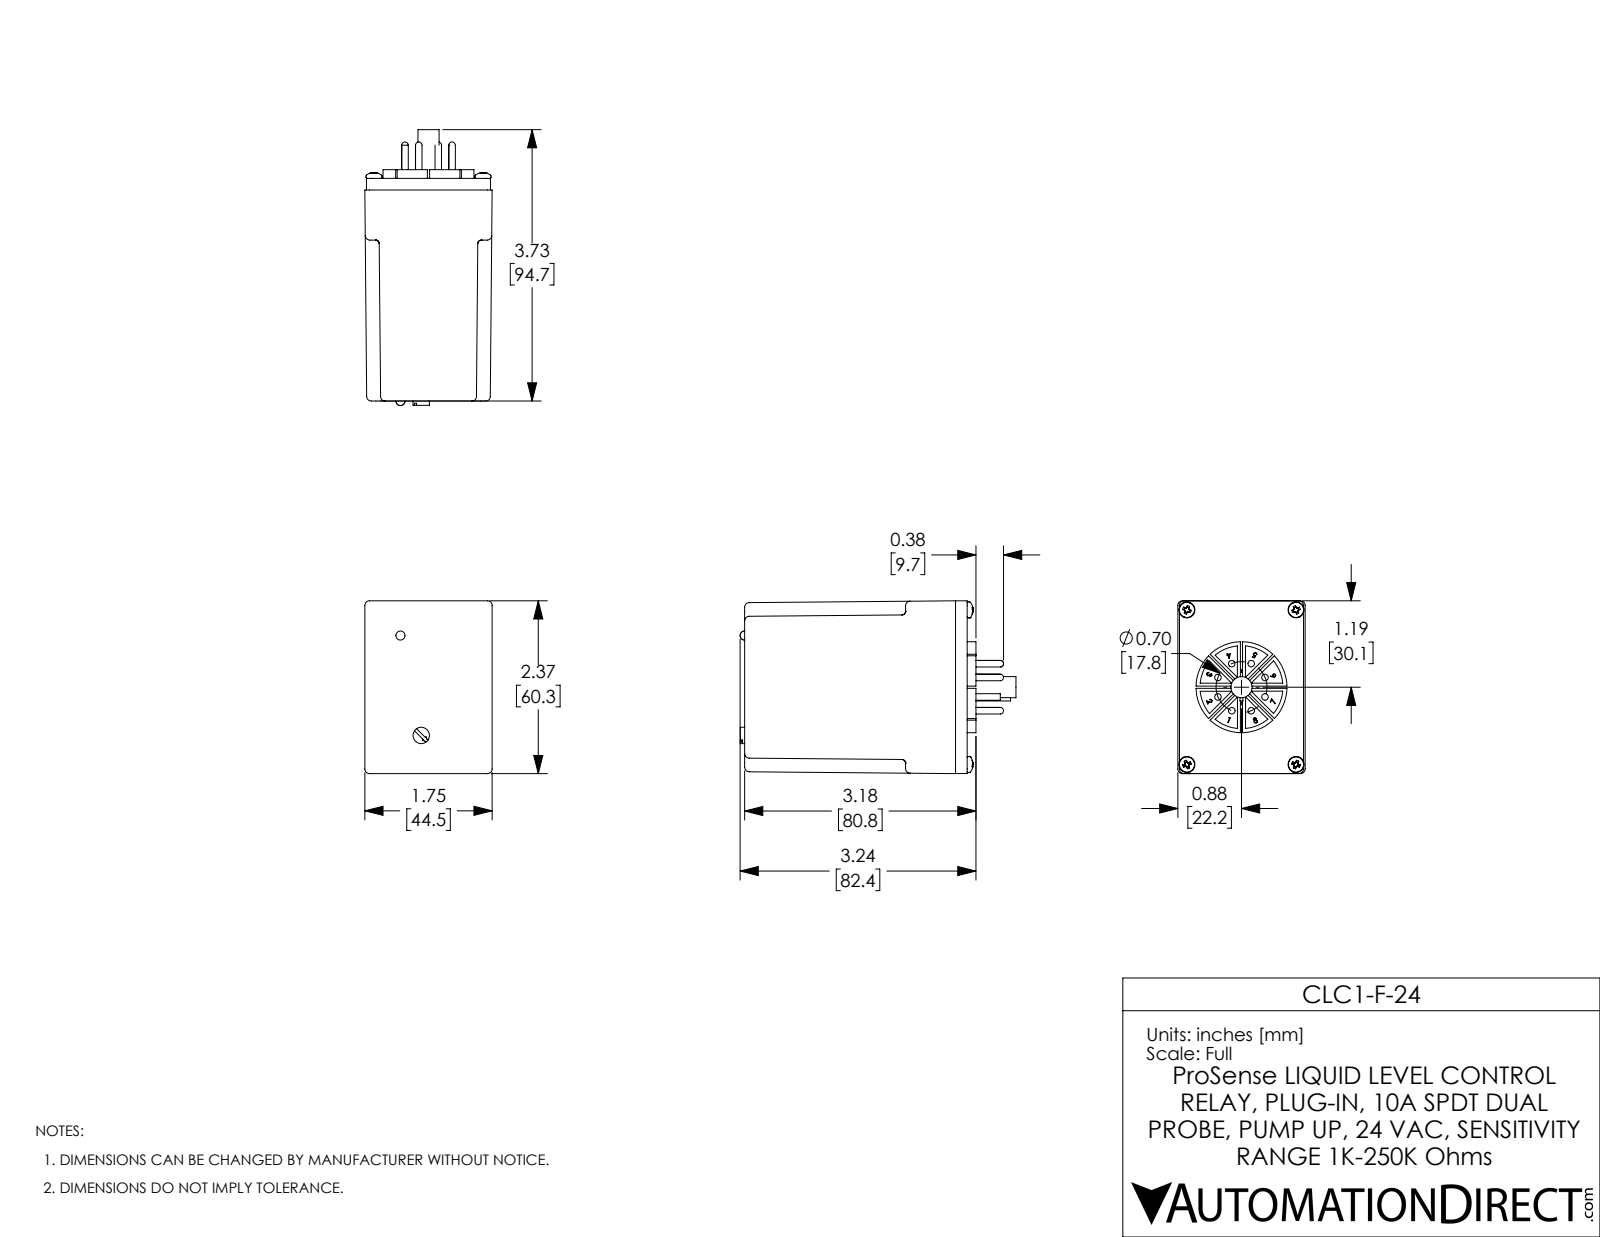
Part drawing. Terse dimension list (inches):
name: CLC1-F-24
written by: SolidWorks 2017 (AUTOMOTIVE_DESIGN)
unit: in
bodies: 16 solids, 706 faces (229 planar, 294 cylindrical, 183 other)
size: 3.79 × 2.375 × 1.75
volume: 12.24 in³; area: 44.72 in²
holes: 4× ⌀0.125
bosses: 8× ⌀0.09, 4× ⌀0.219, 4× ⌀0.112, 4× ⌀0.08, 1× ⌀1.25, 1× ⌀0.29, 1× ⌀0.225
rounds: 32× R0.063, 8× R0.005, 4× R0.05, 1× R0.57
face distances: 2.9, 0.16, 3.06, 0.07, 0.23, 3.13, 0.188, 0.03, 3.18, 0.05
hole spacings: 1.5, 2.125, 2.601
